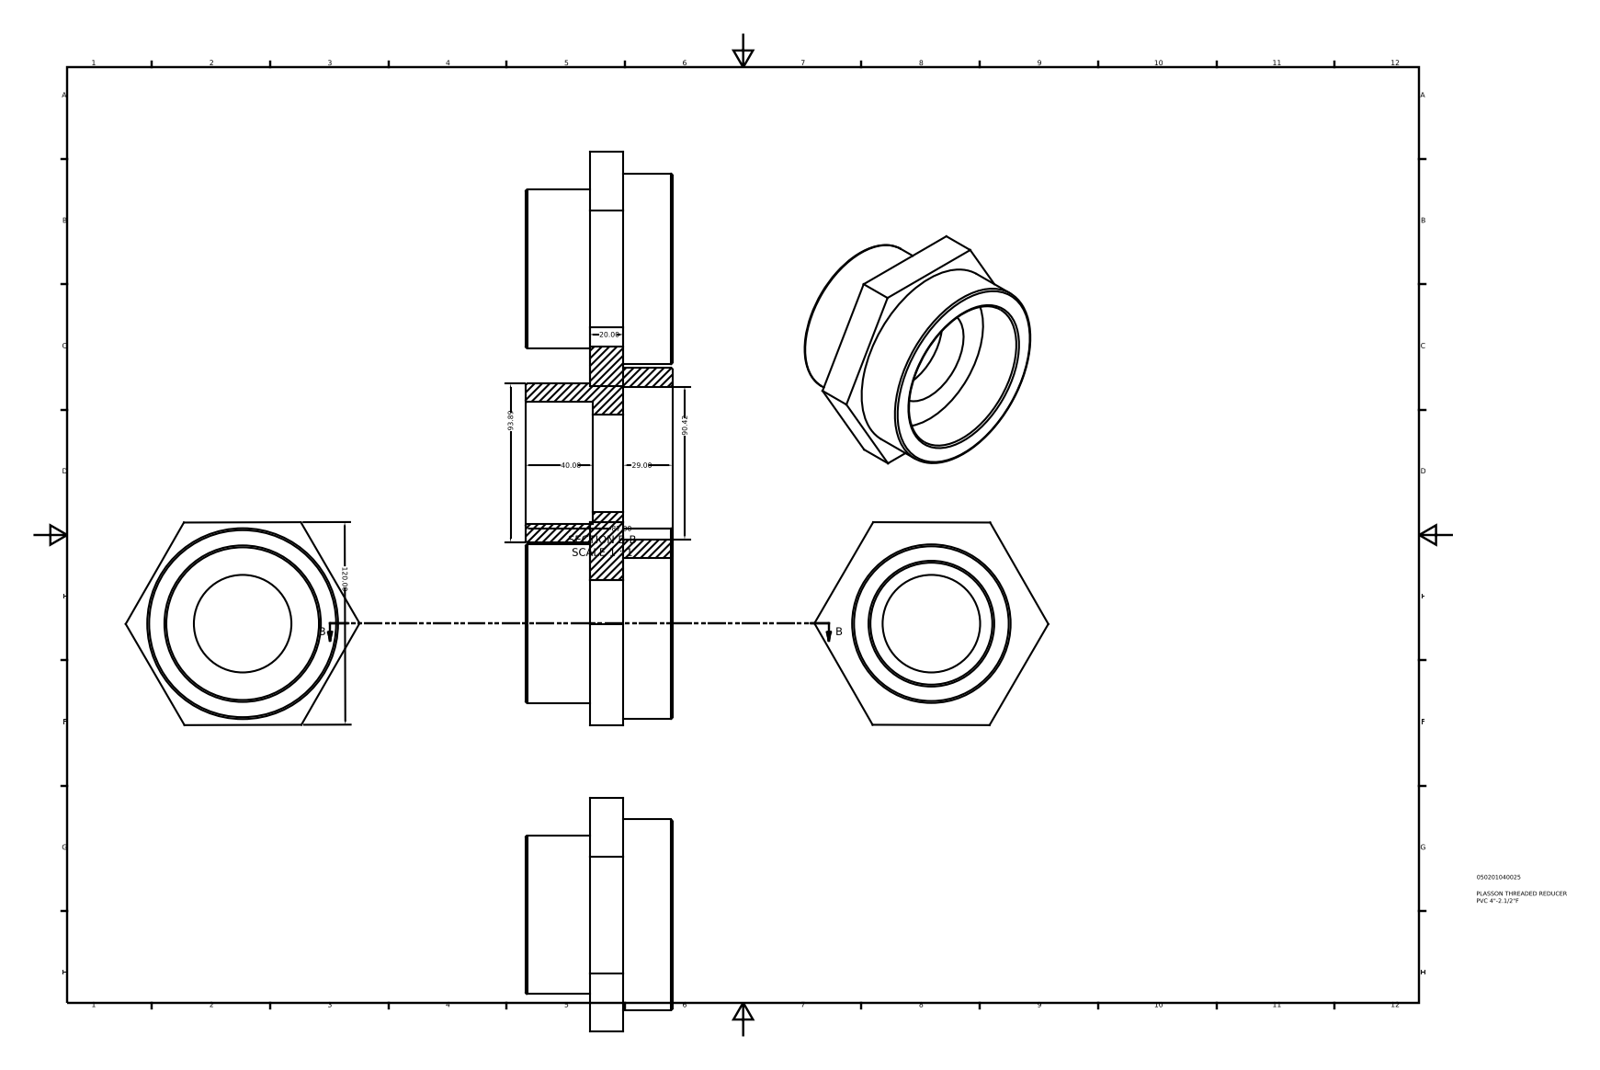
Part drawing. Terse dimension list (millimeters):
name: 050201040025
written by: Autodesk Inventor 2015 (AUTOMOTIVE_DESIGN)
unit: mm
bodies: 1 solid, 21 faces (12 planar, 5 cylindrical, 4 other)
size: 138.56 × 120.2 × 87
volume: 405 886 mm³; area: 69 536 mm²
holes: 1× ⌀57.78, 1× ⌀72.23, 1× ⌀90.42
bosses: 1× ⌀113.03, 1× ⌀93.89
face distances: 20, 49, 29, 38, 58, 87, 40, 2, 18, 47
